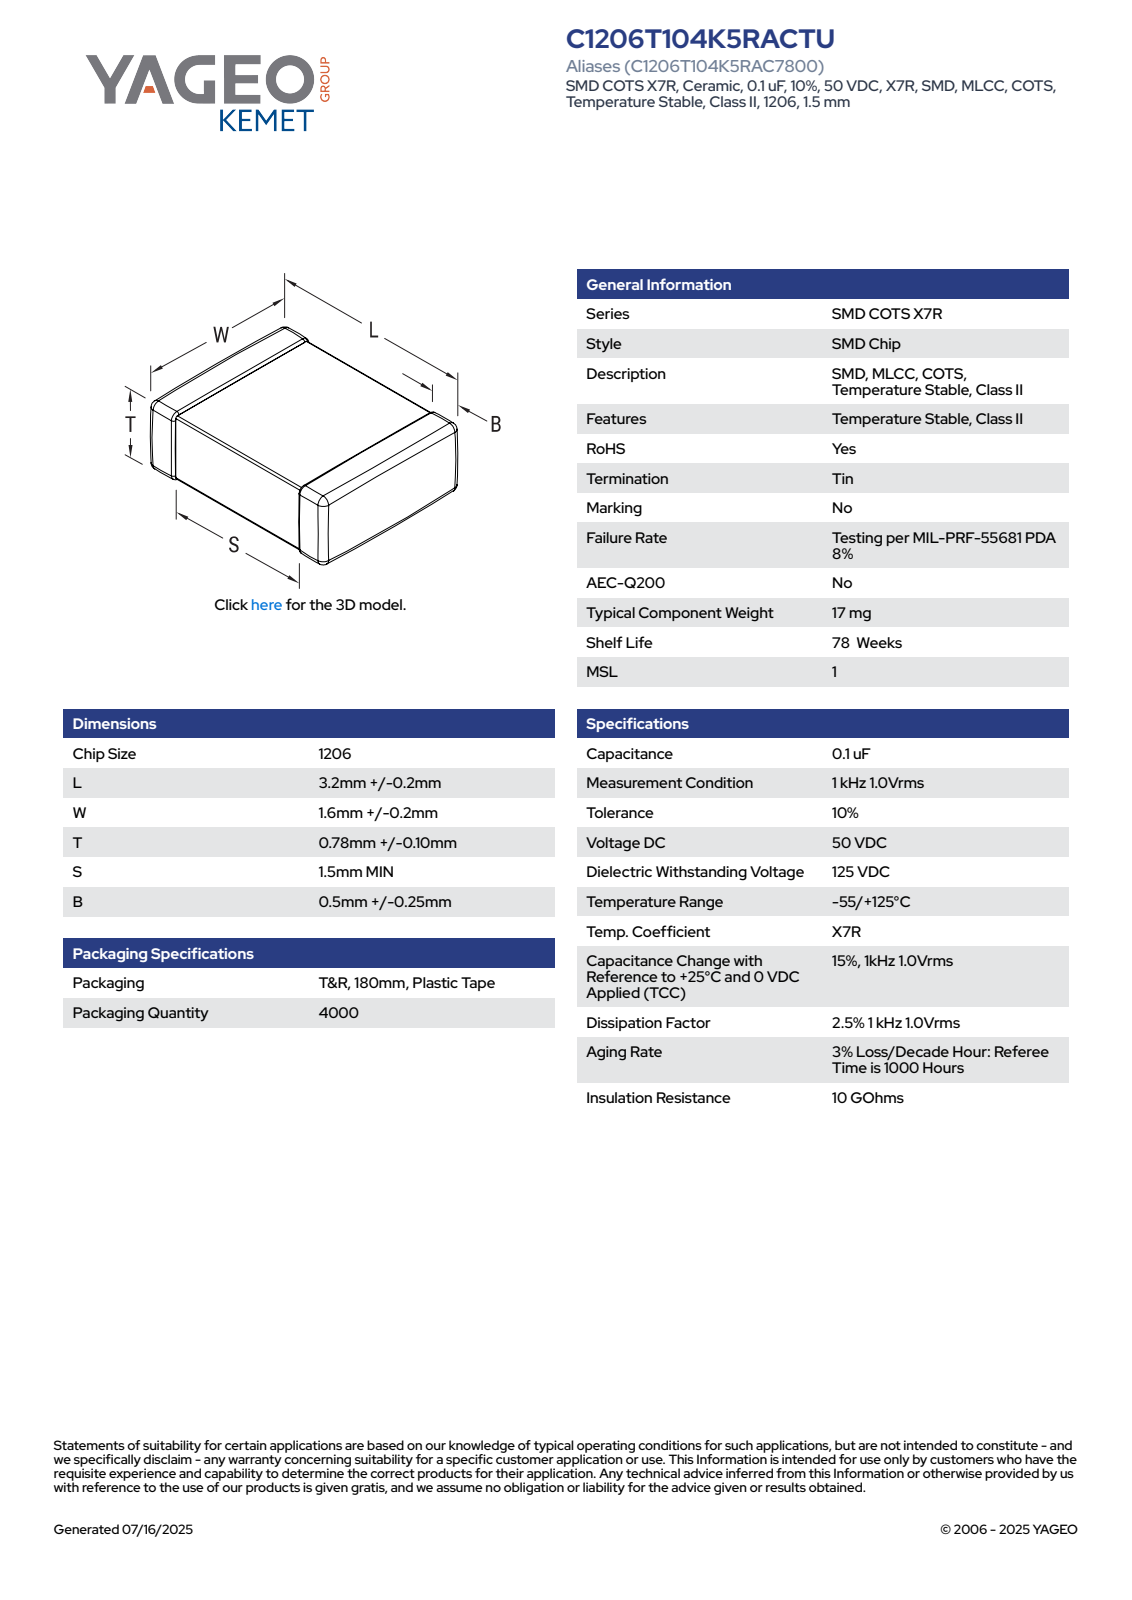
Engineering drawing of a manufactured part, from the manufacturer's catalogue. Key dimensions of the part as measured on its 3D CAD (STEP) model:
Part name (STEP PRODUCT): CCSM_STD_1206_L3.4W1.8T0.88S0.78B0.75
STEP written by: SolidWorks 2021 (AUTOMOTIVE_DESIGN)
Units: millimetres
Bodies: 4 solids, 125 faces (71 planar, 38 cylindrical, 16 other)
Overall size (bounding box): 3.4 × 1.8 × 0.88
Volume: 5 mm³ · Surface area: 21 mm²
Main face-to-face distances: 0.84, 0.8, 0.88, 1.76, 3.4, 1.72, 1.8, 0.85, 0.81, 1.57
